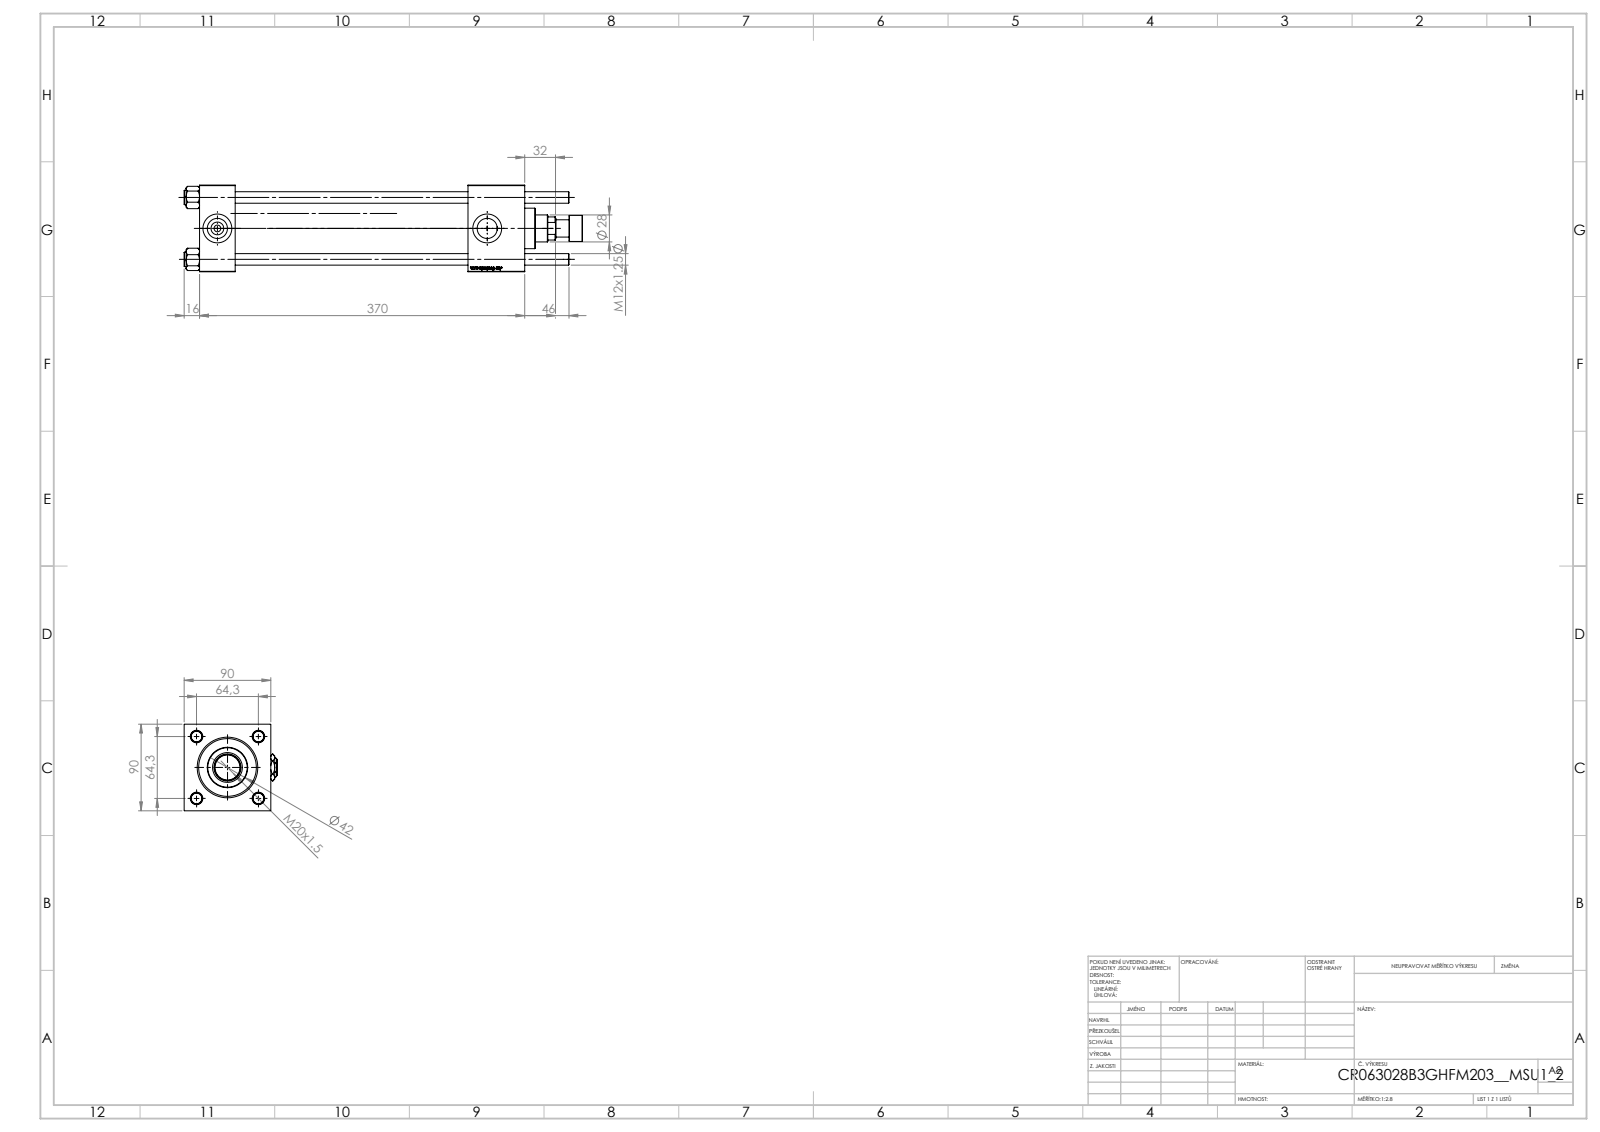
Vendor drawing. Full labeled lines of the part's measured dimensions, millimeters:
Part name (STEP PRODUCT): V215CR_ROD_END_F; V215CR_VCP_B; Zatka_pro_OIL_PORT; V215CR_B_TYCINKA (+3 more)
STEP written by: SolidWorks 2019 (CONFIG_CONTROL_DESIGN)
Units: millimetres
Bodies: 14 solids, 1271 faces (483 planar, 92 cylindrical, 696 other)
Overall size (bounding box): 414 × 97 × 90
Volume: 1 296 000 mm³ · Surface area: 322 637 mm²
Round holes (diameter × count): ⌀12 ×4, ⌀7 ×2, ⌀20.96 ×2, ⌀30 ×2, ⌀18.5 ×1, ⌀28 ×1, ⌀31 ×1, ⌀50 ×1, ⌀60 ×1, ⌀63 ×1
Round bosses / shafts (diameter × count): ⌀15 ×4, ⌀69 ×1, ⌀42 ×1, ⌀27 ×1, ⌀18 ×1
Main face-to-face distances: 90, 37, 301, 338, 59, 279, 242, 309.3, 272.3, 30.3
Hole centre spacings: 45.47, 64.3, 90.93, 280.5
